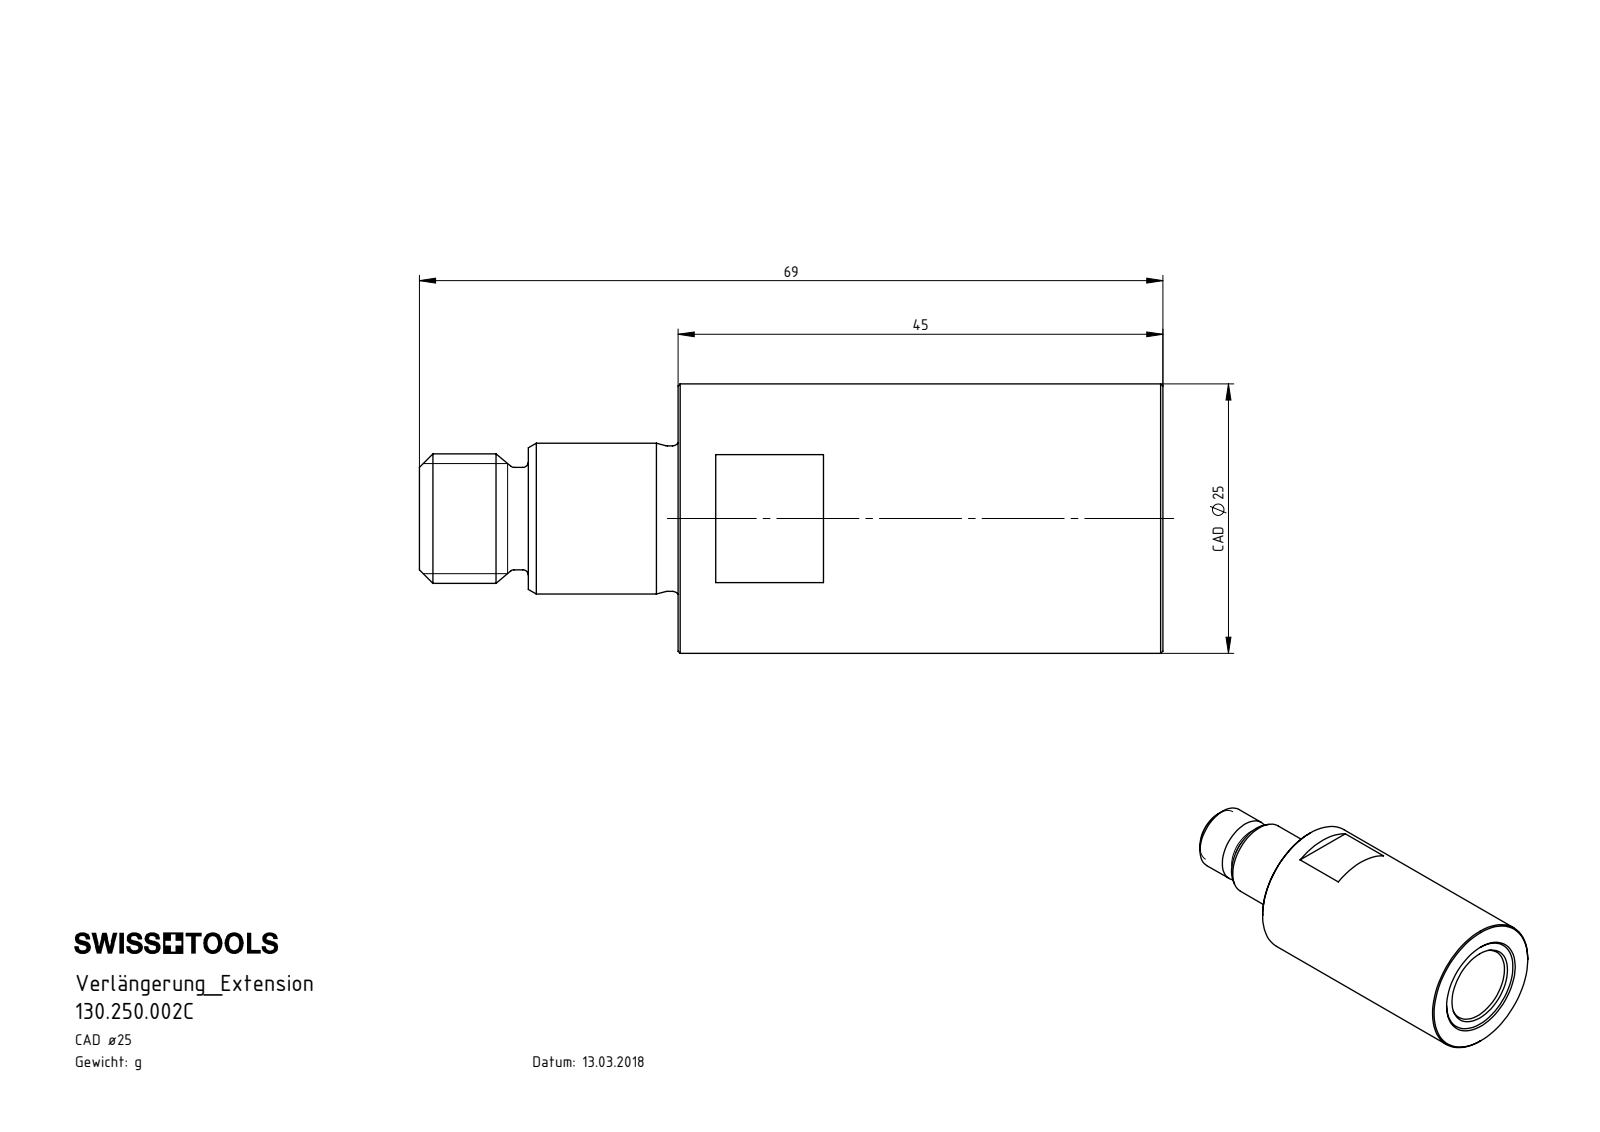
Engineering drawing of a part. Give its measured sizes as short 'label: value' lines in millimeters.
name: 130.250.002C
written by: SolidWorks 2017 (CONFIG_CONTROL_DESIGN)
unit: mm
bodies: 1 solid, 68 faces (12 planar, 18 cylindrical, 38 other)
size: 69 × 25 × 25
volume: 20 872 mm³; area: 7 046 mm²
holes: 1× ⌀3.3, 1× ⌀10.2, 1× ⌀14, 1× ⌀14.5
bosses: 1× ⌀25, 1× ⌀13.5, 1× ⌀12, 1× ⌀9.5
face distances: 45, 22, 44.7, 24, 68.7, 69, 10.1, 13.9, 58.6, 58.9
